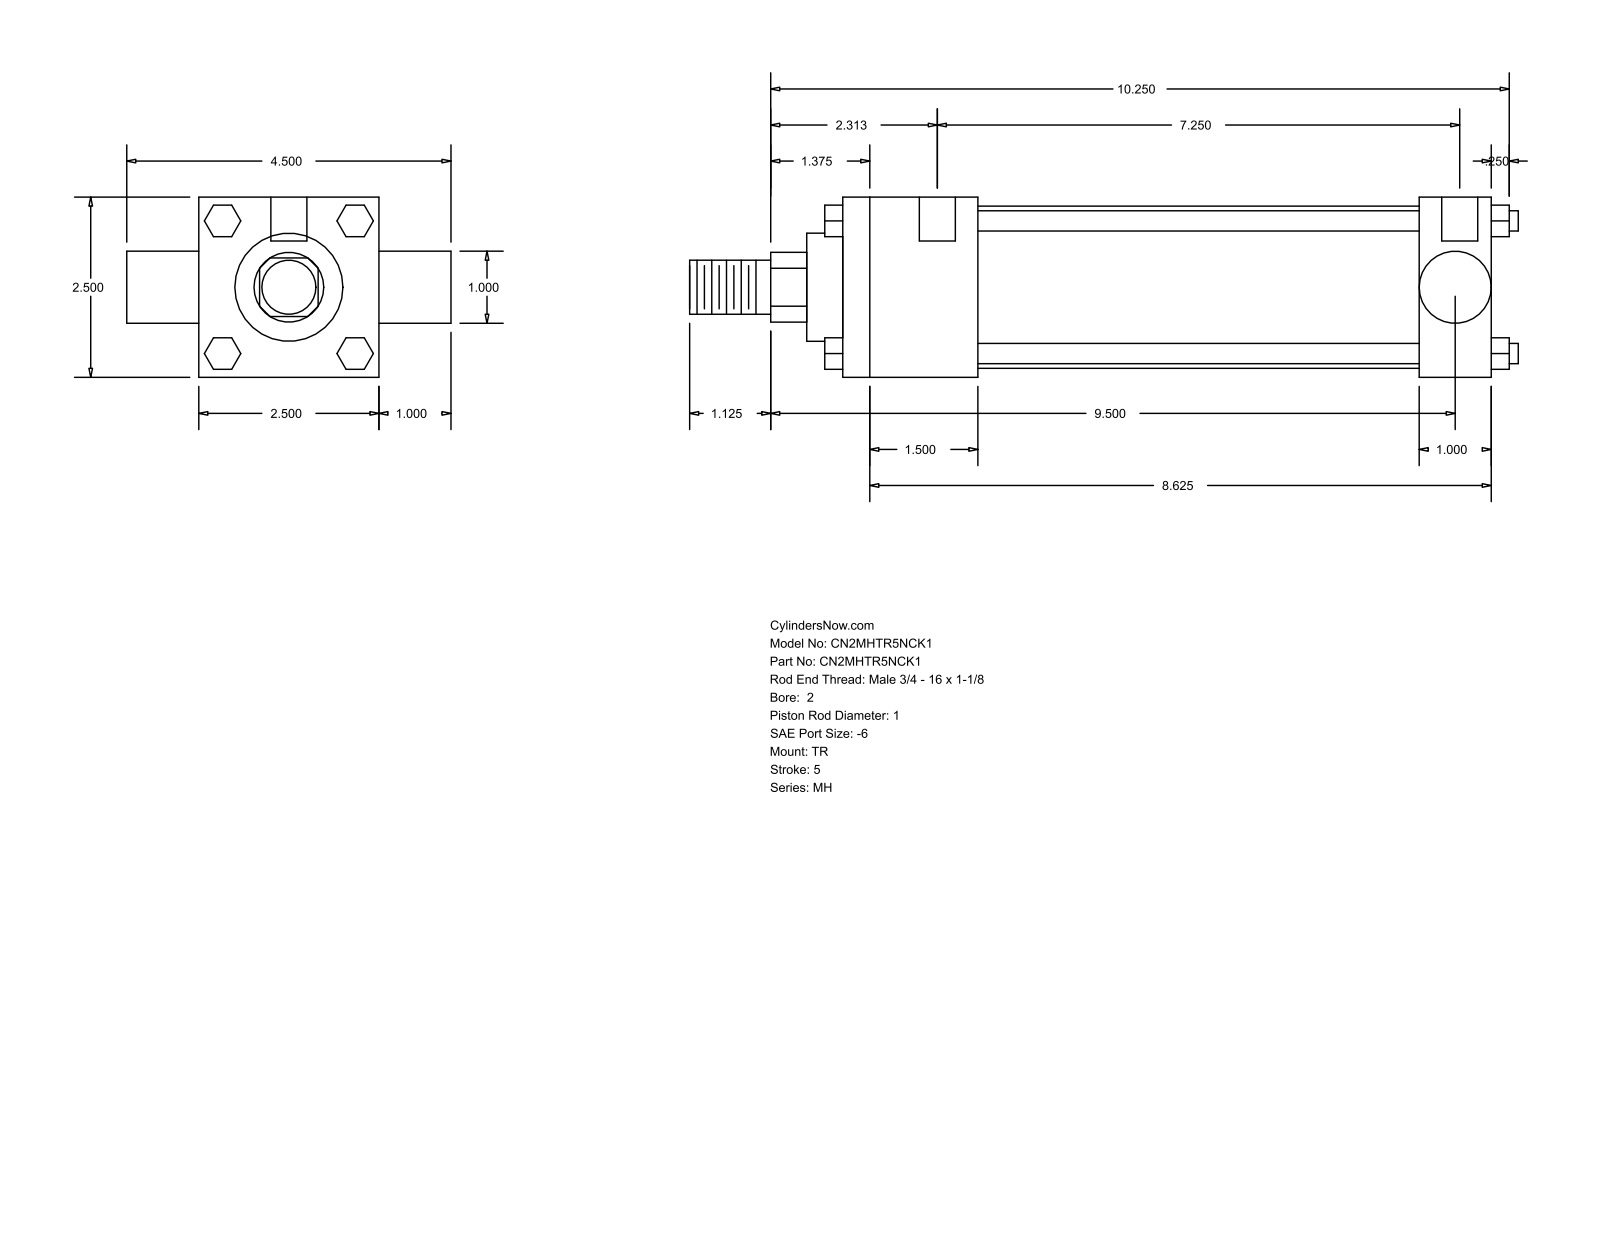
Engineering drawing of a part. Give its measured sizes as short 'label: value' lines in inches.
name: MH_TR__0200_1
written by: GSSL Pune (CONFIG_CONTROL_DESIGN)
unit: in
bodies: 0 solids, 120 faces (92 planar, 28 cylindrical, 0 other)
size: 11.5 × 4.5 × 2.5
holes: 3× ⌀0.219, 2× ⌀0.5
bosses: 4× ⌀0.281, 1× ⌀2.25, 1× ⌀1.5, 1× ⌀1, 1× ⌀0.998, 1× ⌀0.75
rounds: 1× R0.484
face distances: 2.5, 9, 1, 1.875, 8, 6.125, 7.125, 3.5, 9.5, 0.25
hole spacings: 0.125, 0.187, 7.25, 7.375, 7.437, 7.562
